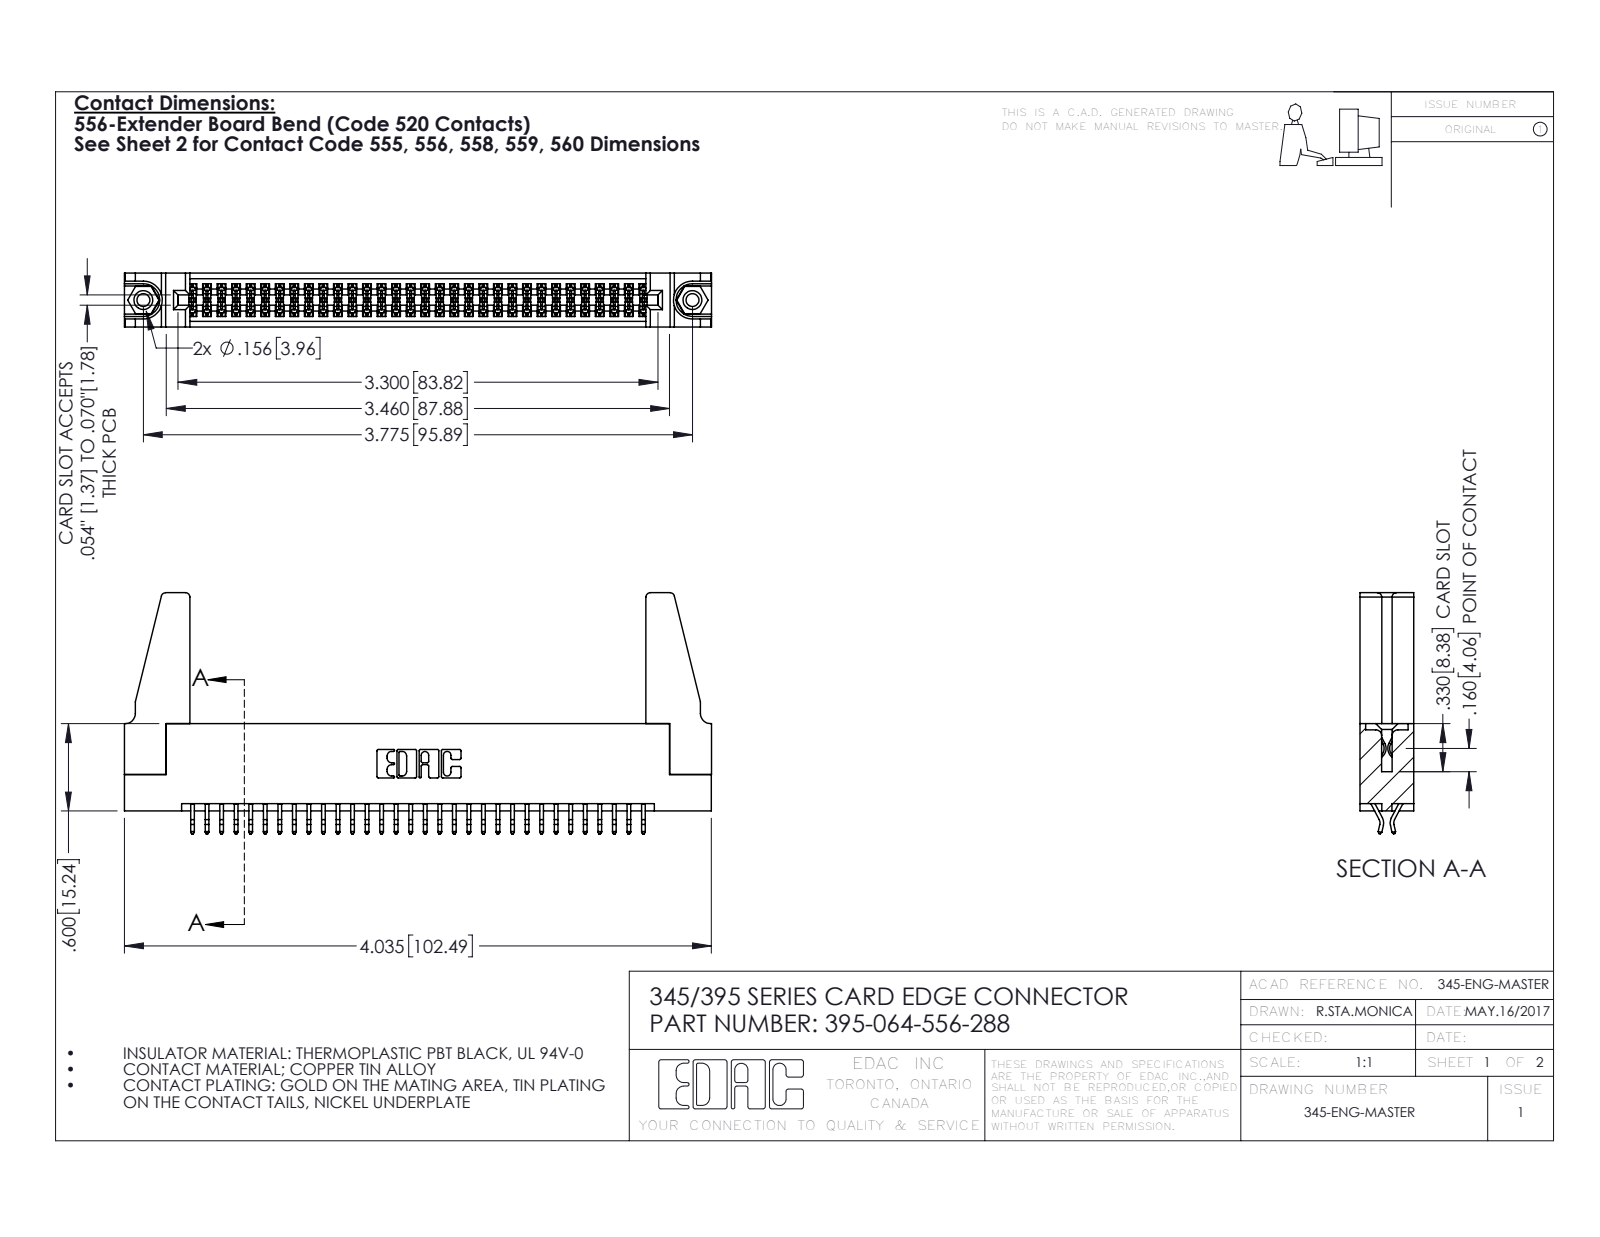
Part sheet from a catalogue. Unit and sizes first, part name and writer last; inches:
Units: inches
Overall size (bounding box): 4.036 × 1.657 × 0.37
Round holes (diameter × count): ⌀0.089 ×2, ⌀0.125 ×2, ⌀0.156 ×2, ⌀0.064 ×1
Round bosses / shafts (diameter × count): ⌀0.155 ×2
Partial cylindrical surfaces — rounded edges, fillets, slot ends (radius × count): R0.006 ×96, R0.01 ×22, R0.03 ×8, R0.007 ×6, R0.031 ×6, R0.026 ×3, R0.01 ×2, R0.014 ×2
Main face-to-face distances: 0.072, 0.298, 0.37, 0.2, 0.025, 0.098, 0.272, 0.225, 0.175, 0.149
Hole centre spacings: 0.27, 3.54, 3.775
Volume: 0.8 in³ · Surface area: 27.05 in²
Bodies: 69 solids, 3834 faces (2520 planar, 1298 cylindrical, 16 other)
Part name (STEP PRODUCT): 345-220-078_345-220-088; 345 Part_Flush Mounting Lugs - 0.156 Dia-TH; 395-064-556-288; 345-292-001_556 Tail (+1 more)
STEP written by: SolidWorks 2016 (CONFIG_CONTROL_DESIGN)
